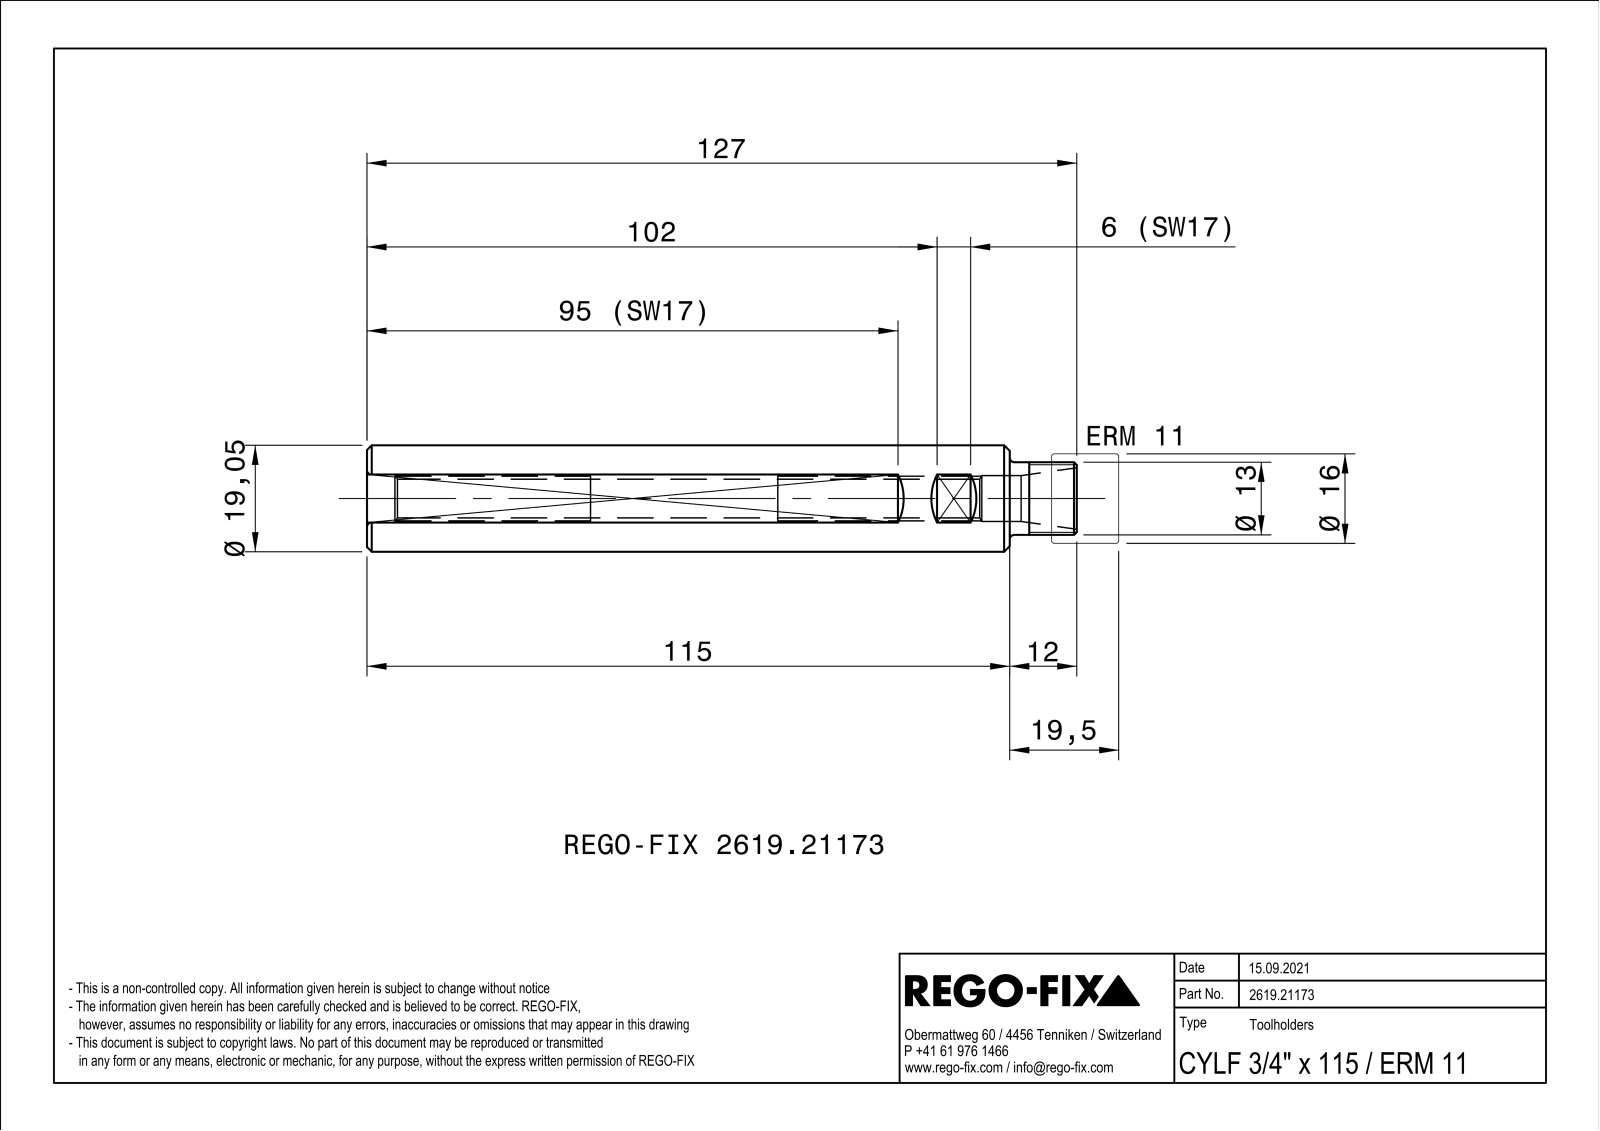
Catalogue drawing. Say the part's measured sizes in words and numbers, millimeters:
The part is named "NOCUT". Its 3-D file was written by "SIEMENS PLM Software Solid Edge ST10 (AUTOMOTIVE_DESIGN)". It is 1 solid with 29 faces: 12 planar, 8 cylindrical and 9 other. Overall it measures 127 by 19.05 by 19.05 millimeters. Its volume is 28 333 cubic millimeters and its surface area 10 577 square millimeters. Round holes: 1 of diameter 6.92, 1 of diameter 8.2, 1 of diameter 8.5. Round bosses or shafts: 1 of diameter 19.05, 1 of diameter 13. The main face-to-face distances are 115, 17, 12, 127, 75.76, 7.78, 9.2, 66.56, 7.77, 16.97.
